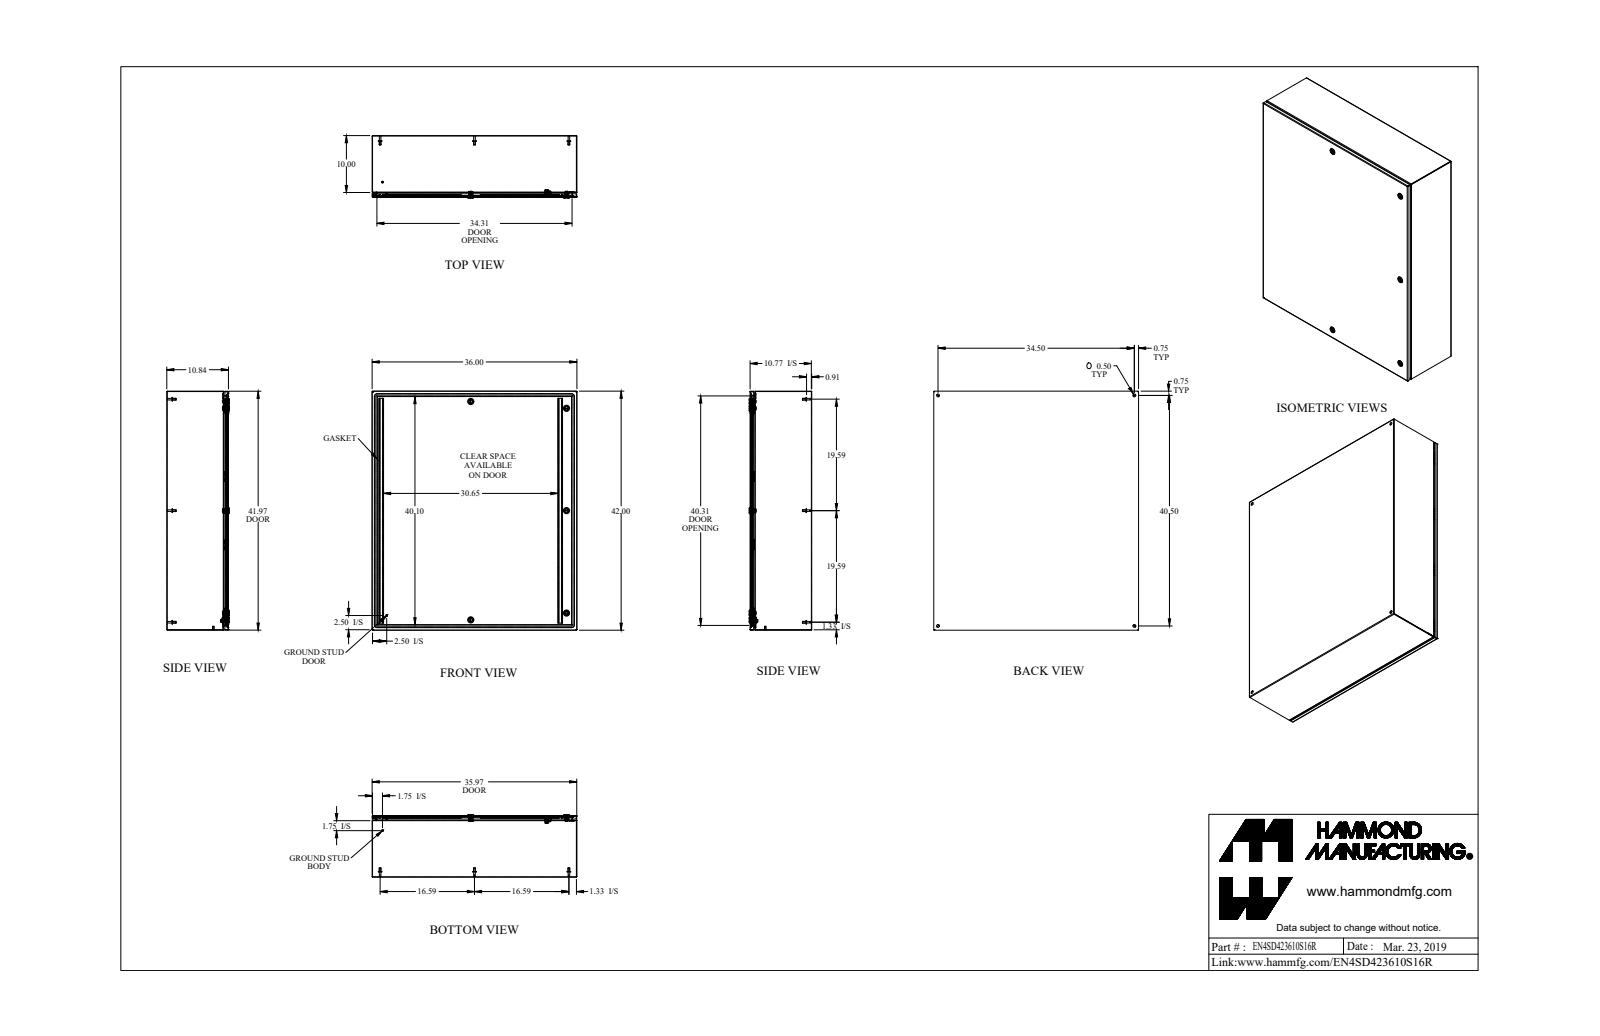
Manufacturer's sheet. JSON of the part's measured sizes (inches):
{"part_name": "EN4SD423610S16R", "step_written_by": "SolidWorks 2019 (AUTOMOTIVE_DESIGN)", "units": "inches", "bodies": {"solids": 64, "faces": 1733, "planar": 896, "cylindrical": 552, "other": 285}, "overall_size": [42, 36, 11.001], "volume_in3": 381.2, "surface_area_in2": 10741, "round_holes": [[0.5, 9], [0.197, 5], [0.387, 5], [0.63, 5], [0.768, 5], [0.172, 1], [0.196, 1], [0.24, 1], [0.242, 1], [0.275, 1], [0.375, 1]], "round_bosses_or_shafts": [[0.313, 10], [0.625, 7], [0.625, 7], [1.1, 5], [0.275, 5], [0.236, 5], [0.525, 4], [0.785, 3]], "partial_cylinders_radius": [[0.01, 24], [0.048, 24], [0.036, 20], [0.108, 20], [0.062, 12], [0.094, 10], [0.125, 10], [0.016, 9]], "face_to_face_distances": [0.072, 10.769, 10.697, 10.841, 35.928, 41.928, 35.856, 36, 41.856, 42], "hole_center_spacings": [2.507, 16.622, 16.881, 17.943, 17.985, 20.278, 25.529, 33.504]}
